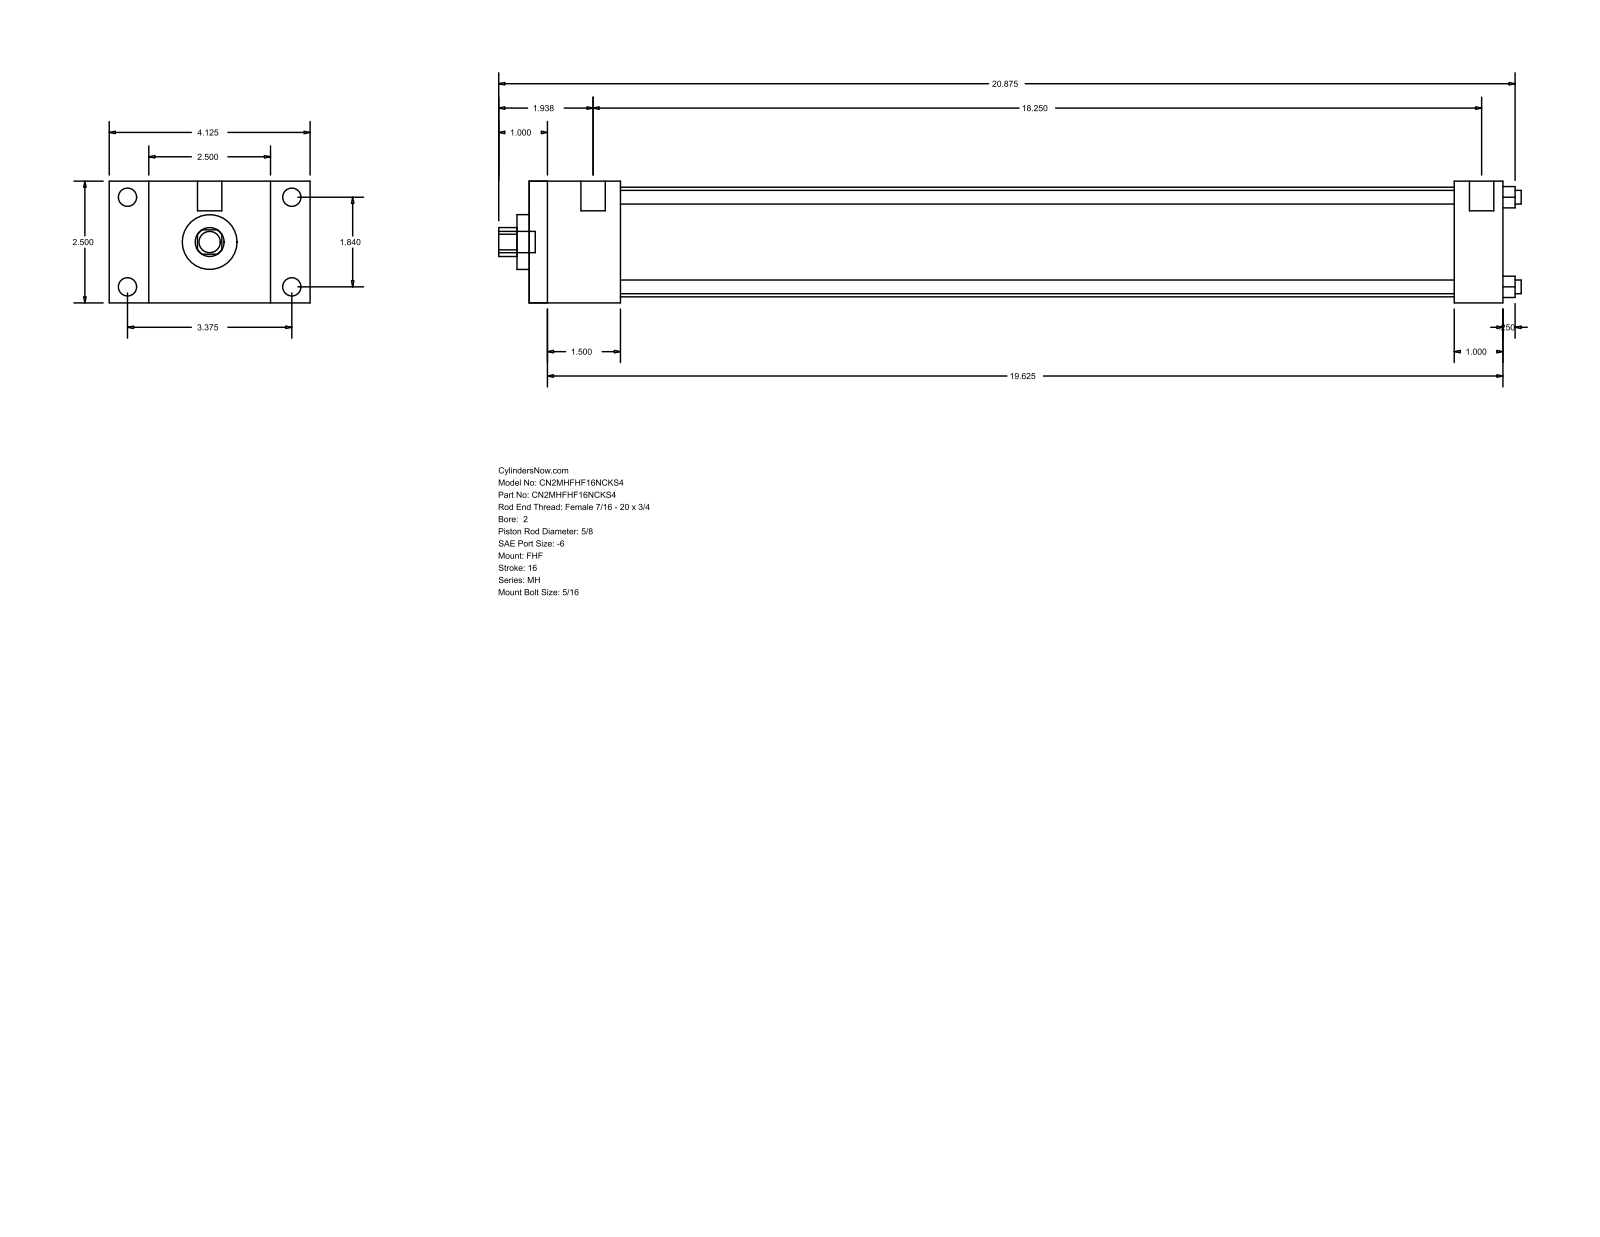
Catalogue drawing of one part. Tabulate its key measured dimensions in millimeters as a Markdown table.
| quantity | value |
| --- | --- |
| part name | MH_FHF__0200_0.625 |
| STEP written by | GSSL Pune (CONFIG_CONTROL_DESIGN) |
| units | millimeters |
| bodies | 0 solids, 88 faces (60 planar, 28 cylindrical, 0 other) |
| overall size | 533.4 × 104.78 × 63.5 |
| round holes (diameter × count) | 7.14 × 4, 15.88 × 1, 28.57 × 1, 57.15 × 1 |
| round bosses / shafts (diameter × count) | 9.53 × 4, 5.56 × 4, 12.7 × 2, 11.11 × 1 |
| partial cylindrical surfaces (radius × count) | 7.54 × 1 |
| main face-to-face distances | 63.5, 47.62, 508, 460.38, 20.64, 84.14, 104.78, 25.4, 482.6, 434.98 |
| hole center spacings | 33.05, 46.74, 66.1 |
